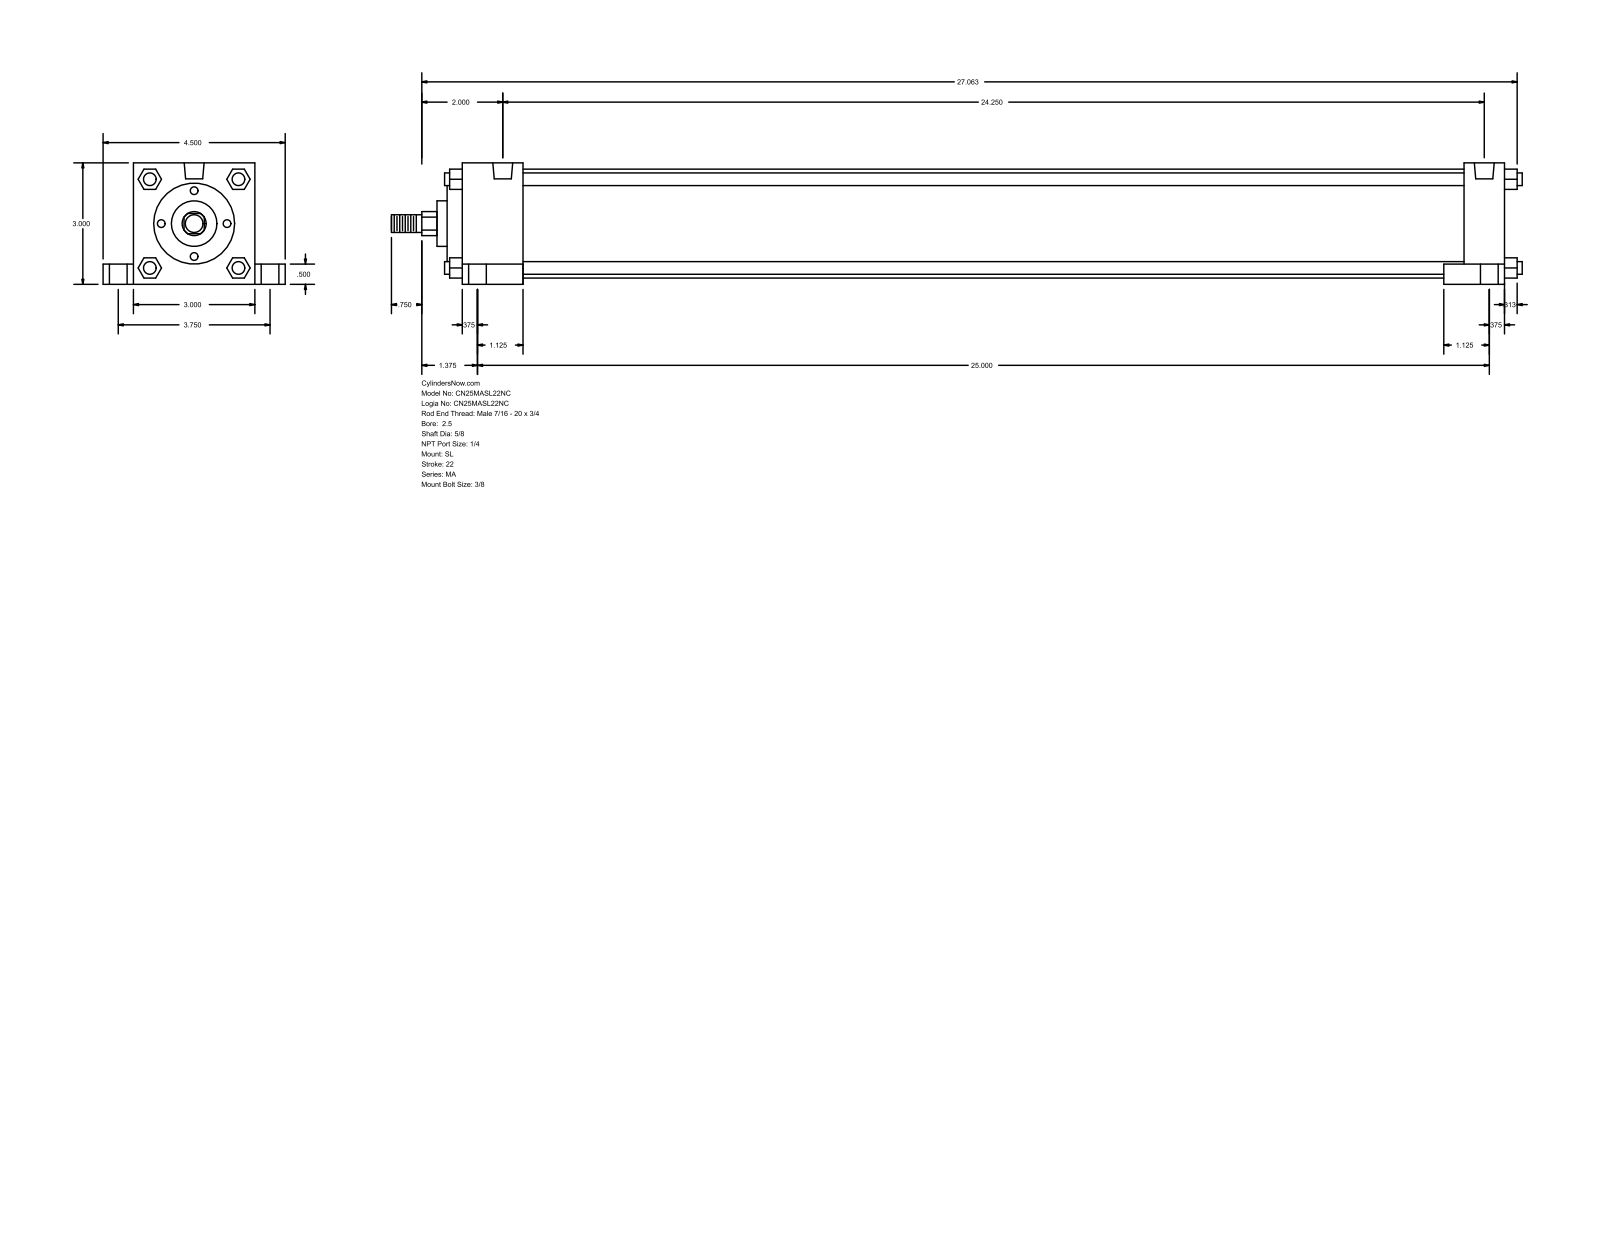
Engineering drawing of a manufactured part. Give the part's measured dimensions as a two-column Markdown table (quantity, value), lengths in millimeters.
| quantity | value |
| --- | --- |
| part name | MA_SL__0250_0.625 |
| STEP written by | GSSL Pune (CONFIG_CONTROL_DESIGN) |
| units | millimeters |
| bodies | 0 solids, 150 faces (113 planar, 37 cylindrical, 0 other) |
| overall size | 709.61 × 114.3 × 76.2 |
| round holes (diameter × count) | 7.94 × 4, 11.11 × 4, 17.46 × 4, 12.49 × 2 |
| round bosses / shafts (diameter × count) | 7.94 × 4, 68.33 × 1, 50.8 × 1, 28.57 × 1, 15.88 × 1, 11.11 × 1 |
| partial cylindrical surfaces (radius × count) | 7.54 × 1 |
| main face-to-face distances | 76.2, 654.05, 12.7, 590.55, 25.4, 38.1, 615.95, 628.65, 19.05, 63.5 |
| hole center spacings | 47.73, 50.2, 95.24, 615.95, 620.95, 633.62, 635, 642.1 |
